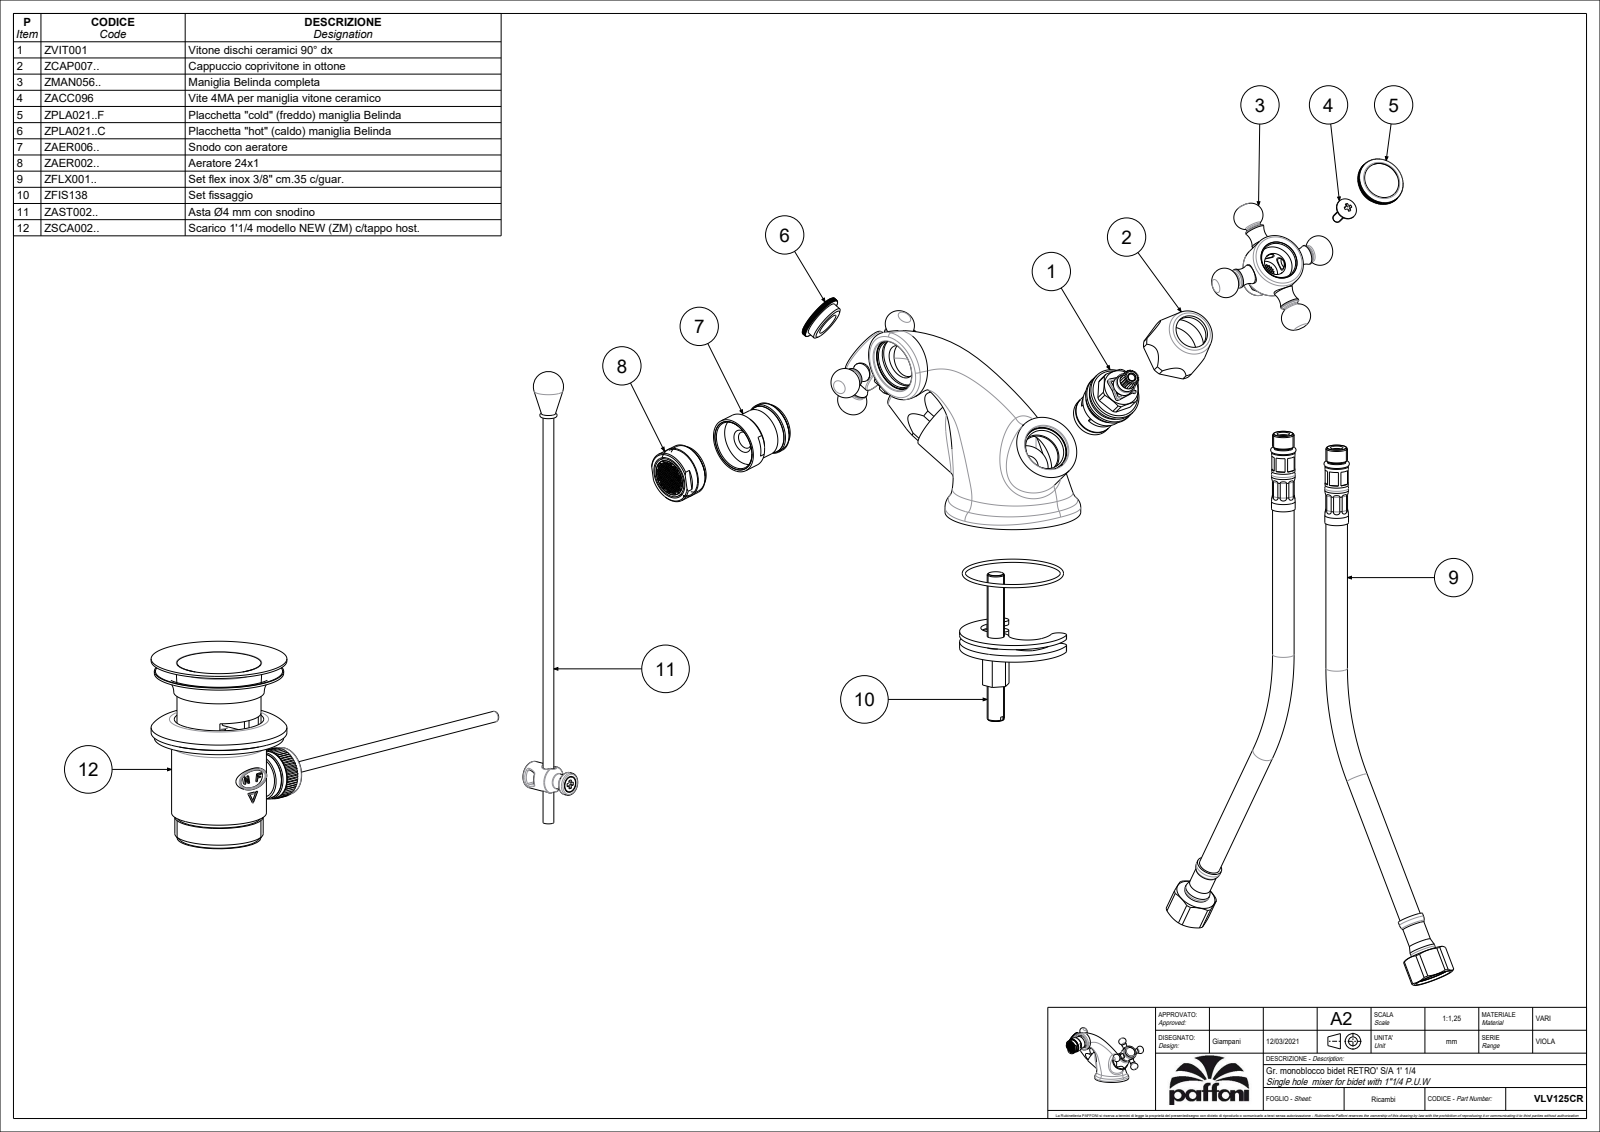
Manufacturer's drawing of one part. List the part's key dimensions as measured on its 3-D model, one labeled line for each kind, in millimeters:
Part name (STEP PRODUCT): VLV125CR
STEP written by: CREO PARAMETRIC BY PTC INC, 2020044 (CONFIG_CONTROL_DESIGN)
Units: millimetres
Bodies: 2 solids, 1074 faces (512 planar, 341 cylindrical, 221 other)
Overall size (bounding box): 178.78 × 140.76 × 101.25
Volume: 160 116 mm³ · Surface area: 61 050 mm²
Round holes (diameter × count): ⌀9 ×4, ⌀11 ×2, ⌀21 ×2, ⌀21.5 ×2, ⌀5.5 ×1, ⌀6.8 ×1, ⌀8 ×1, ⌀15.5 ×1, ⌀16.5 ×1, ⌀49 ×1
Round bosses / shafts (diameter × count): ⌀9 ×8, ⌀7 ×8, ⌀28 ×2, ⌀25 ×2, ⌀19 ×2, ⌀14 ×2, ⌀13 ×2, ⌀63 ×1
Partial cylindrical surfaces — rounded edges, fillets, slot ends (radius × count): R11 ×2, R14.5 ×2, R5 ×1
Main face-to-face distances: 8.5, 35.31, 11.2, 57.19, 21.88, 28.71, 7.2, 1.3, 25.7, 3.01
Hole centre spacings: 7.5, 12.66, 13.48, 10.2, 11.2, 15, 21.4
